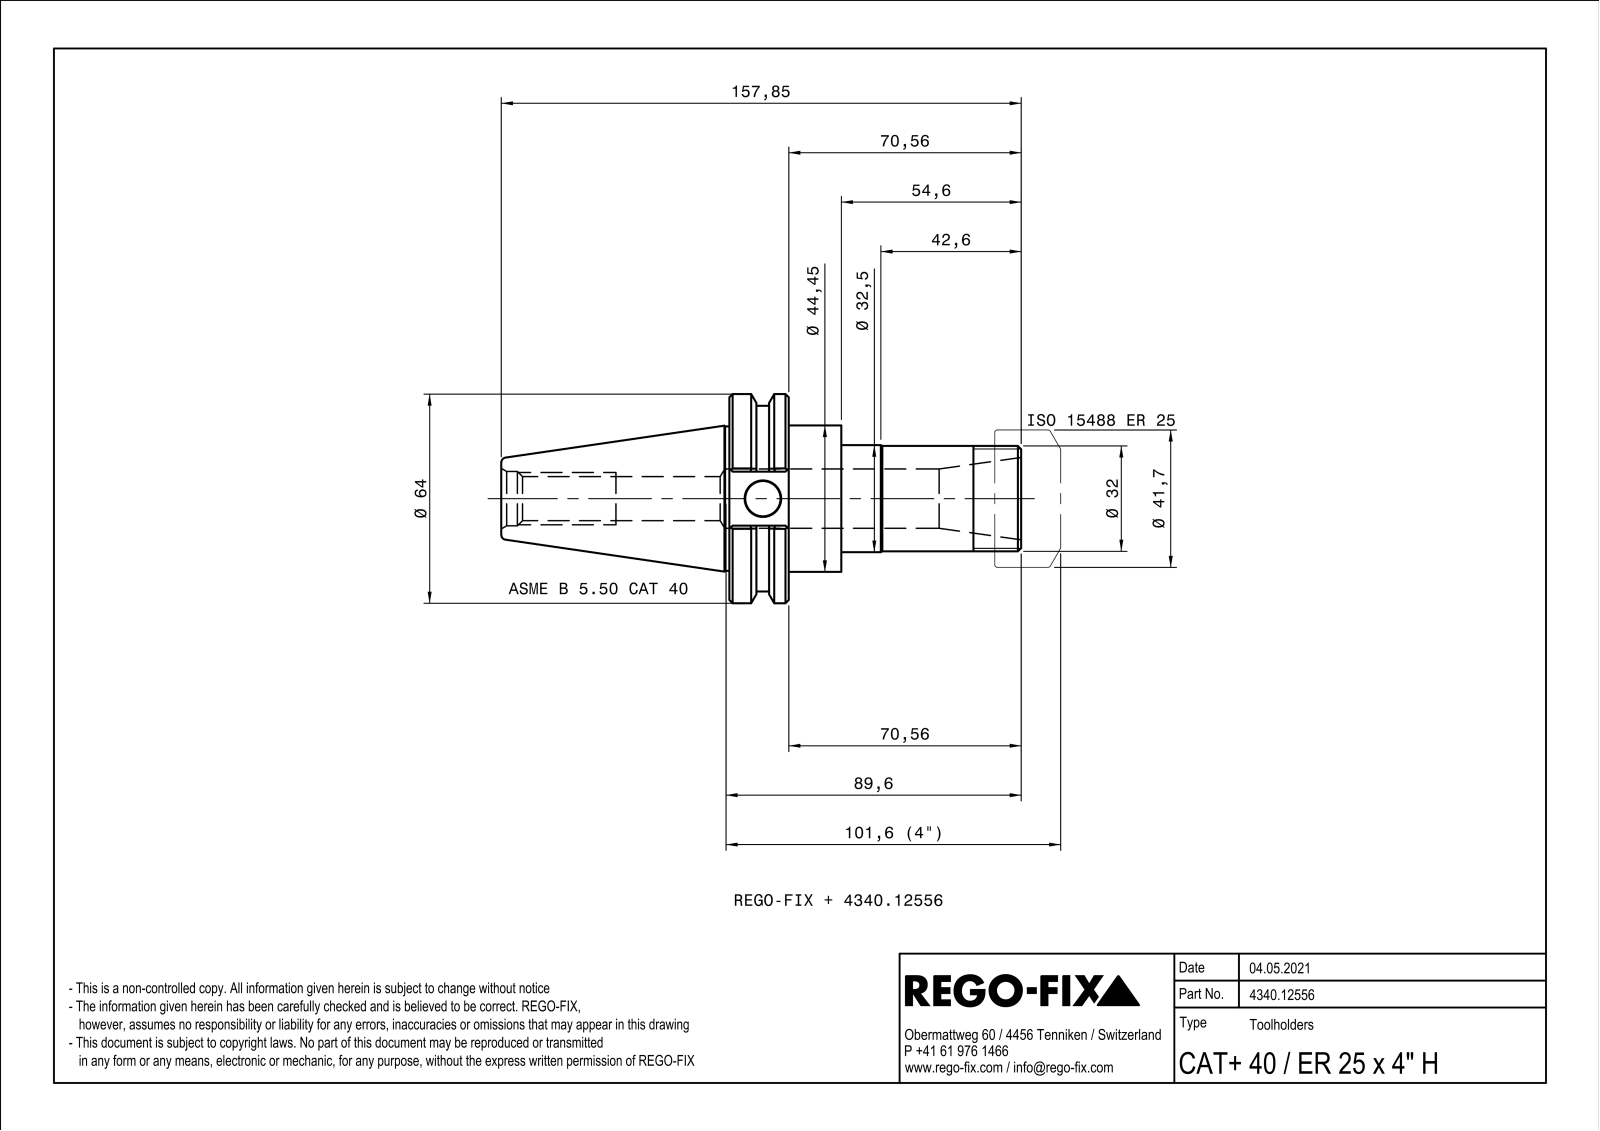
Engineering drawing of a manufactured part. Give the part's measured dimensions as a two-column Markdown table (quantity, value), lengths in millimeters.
| quantity | value |
| --- | --- |
| part name | NOCUT |
| STEP written by | SIEMENS PLM Software Solid Edge ST10 (AUTOMOTIVE_DESIGN) |
| units | millimeters |
| bodies | 2 solids, 215 faces (70 planar, 59 cylindrical, 86 other) |
| overall size | 158.25 × 63.8 × 61.04 |
| volume | 300 104 mm³ |
| surface area | 65 688 mm² |
| round holes (diameter × count) | 3.9 × 2, 3.24 × 1, 12 × 1, 13.38 × 1, 16.2 × 1, 16.5 × 1, 18 × 1 |
| round bosses / shafts (diameter × count) | 63.8 × 1, 63.5 × 1, 56.36 × 1, 44.75 × 1, 44.45 × 1, 43.85 × 1, 32.8 × 1, 32.5 × 1 |
| partial cylindrical surfaces (radius × count) | 0.5 × 4, 2.25 × 2 |
| main face-to-face distances | 18.05, 18.25, 34.2, 15.95, 34, 16.15, 34.4, 54.6, 88.8, 47.33 |
